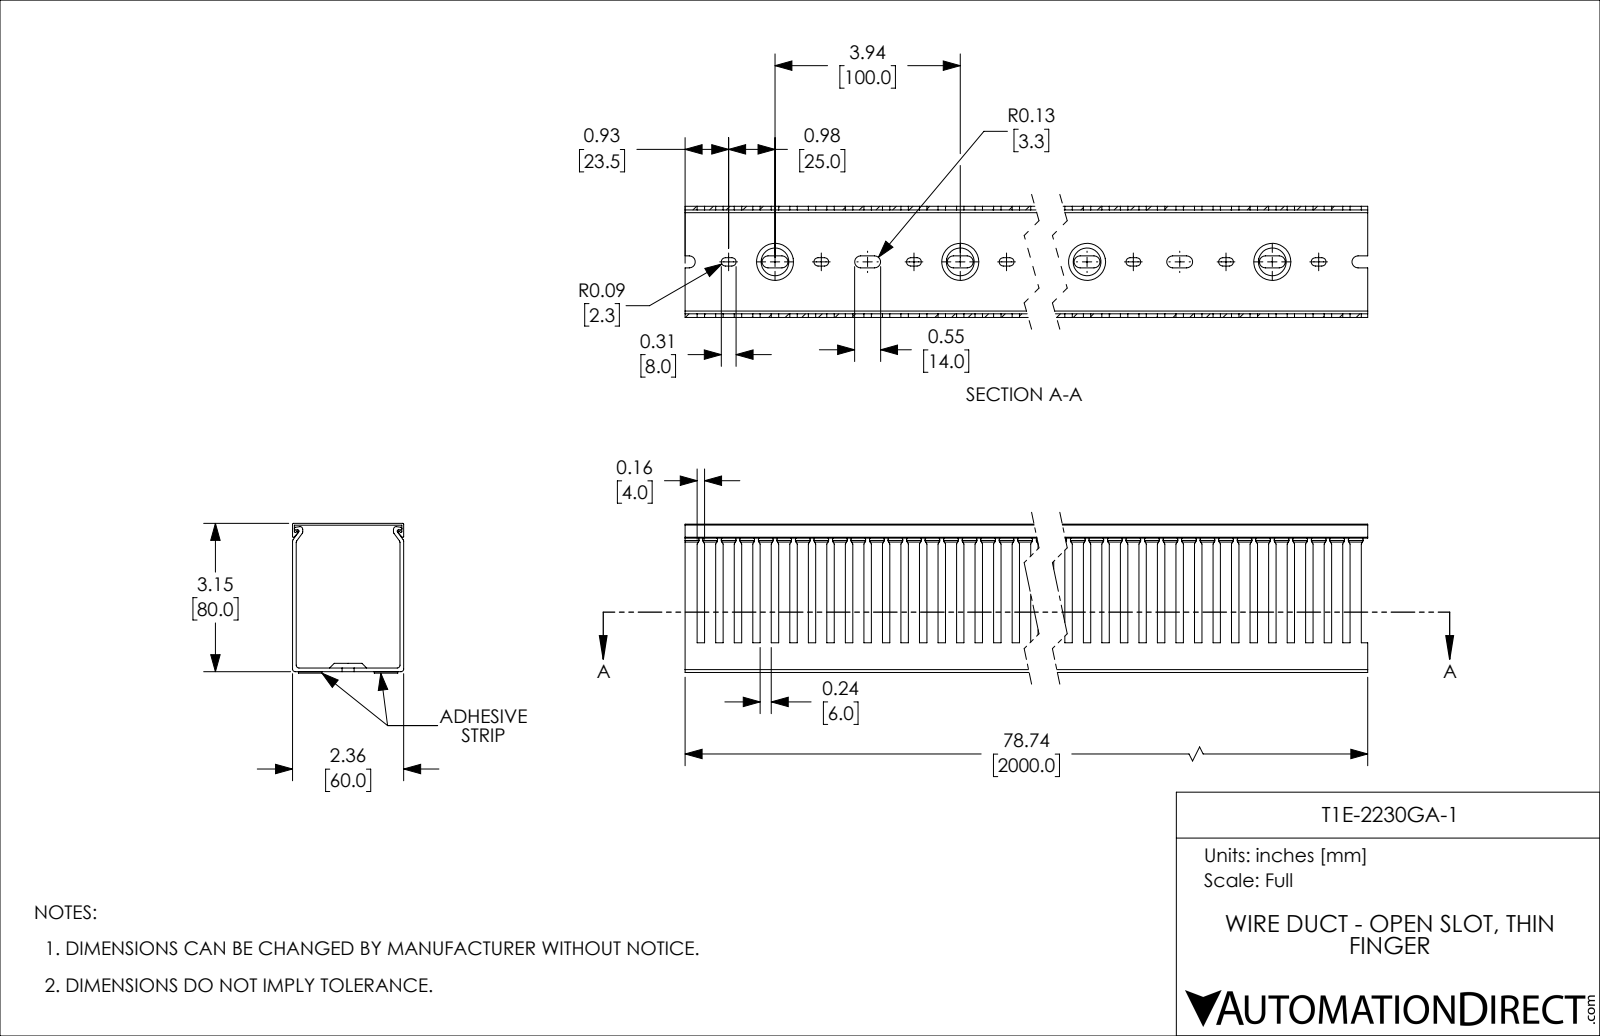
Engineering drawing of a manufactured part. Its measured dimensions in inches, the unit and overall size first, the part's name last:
Units: inches
Overall size (bounding box): 78.74 × 3.181 × 2.362
Partial cylindrical surfaces — rounded edges, fillets, slot ends (radius × count): R0.089 ×80, R0.128 ×80, R0.059 ×12, R0.02 ×8, R0.03 ×6
Main face-to-face distances: 0.079, 2.283, 2.362, 0.039, 2.205, 3.15, 3.11, 3.031, 3.071, 0.031
Volume: 64.69 in³ · Surface area: 1 993 in²
Bodies: 4 solids, 1017 faces (546 planar, 431 cylindrical, 40 other)
Part name (STEP PRODUCT): T1E-2230GA-1
STEP written by: SolidWorks 2021 (CONFIG_CONTROL_DESIGN)
